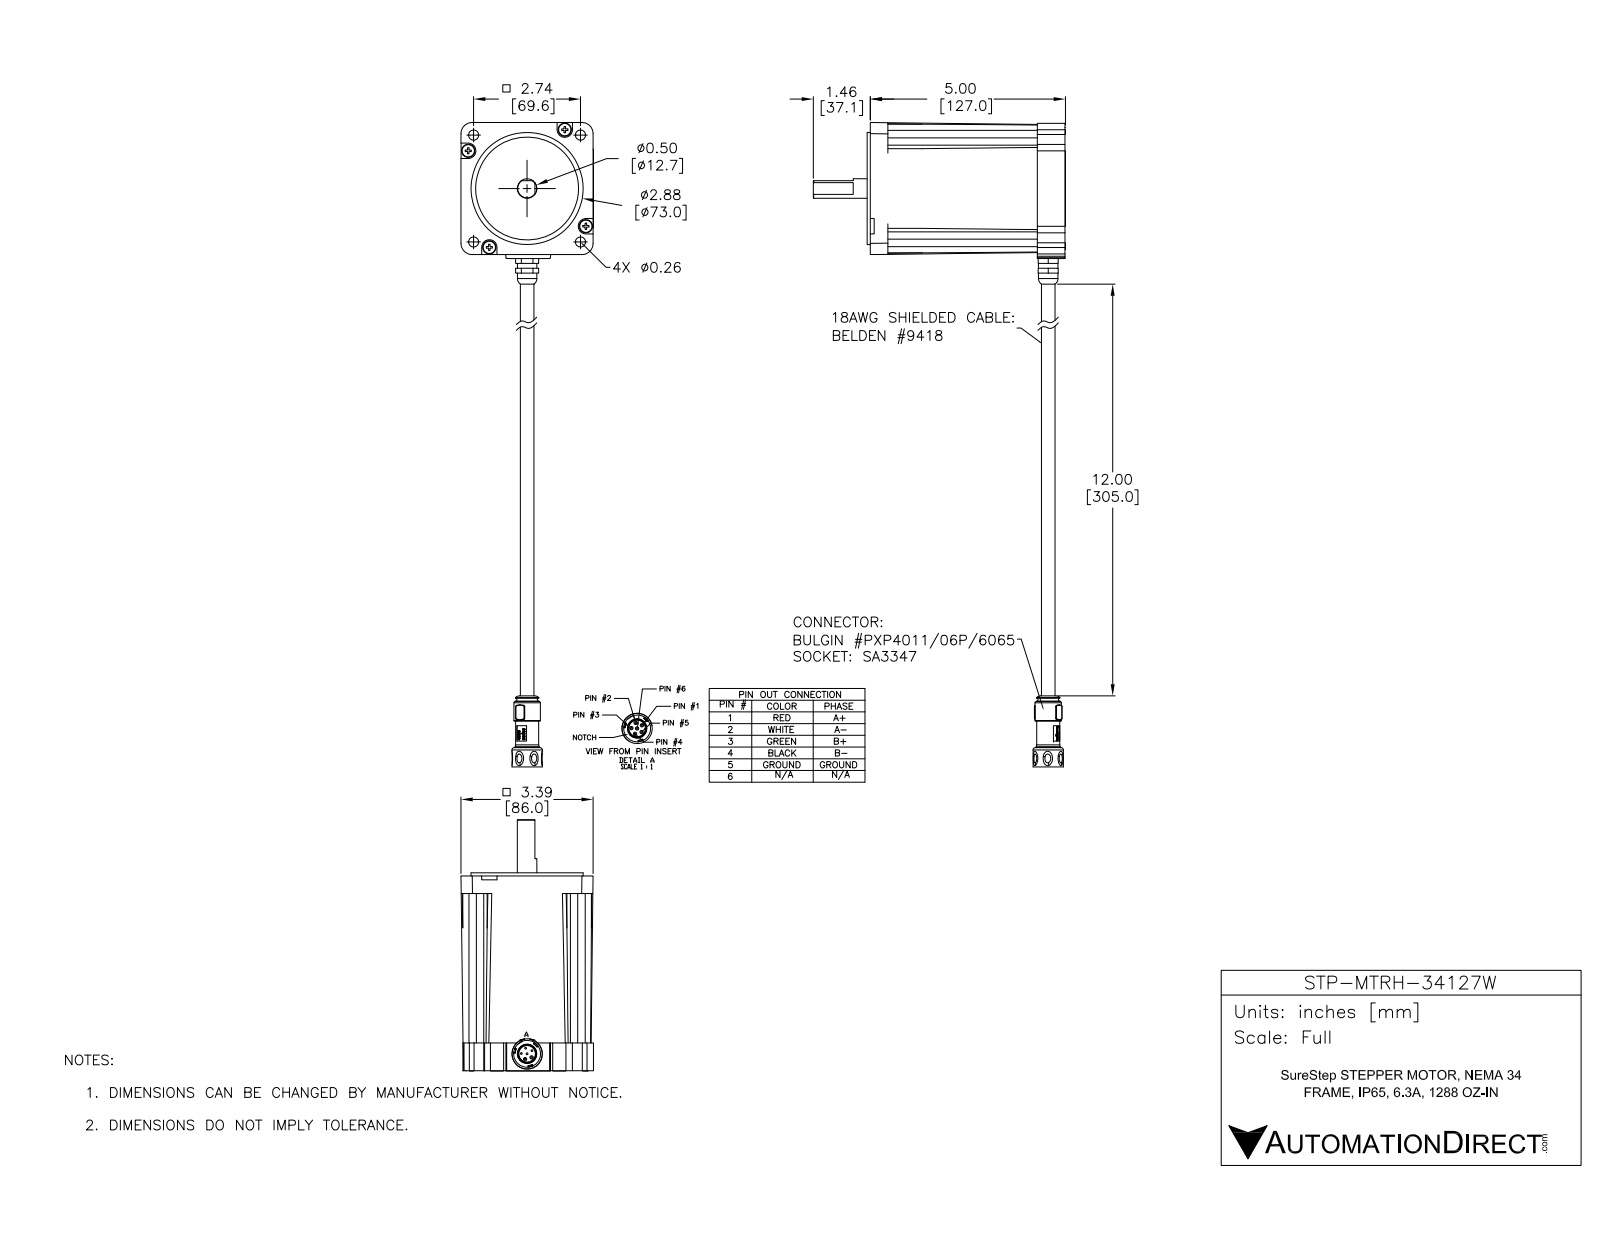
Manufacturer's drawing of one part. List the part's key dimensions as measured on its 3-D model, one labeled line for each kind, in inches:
Part name (STEP PRODUCT): STP-MTRH-34127W
STEP written by: SolidWorks 2017 (AUTOMOTIVE_DESIGN)
Units: inches
Bodies: 3 solids, 840 faces (309 planar, 234 cylindrical, 297 other)
Overall size (bounding box): 16.516 × 6.441 × 3.395
Volume: 52.13 in³ · Surface area: 113.2 in²
Round holes (diameter × count): ⌀0.047 ×6, ⌀0.26 ×4, ⌀0.125 ×1, ⌀0.228 ×1, ⌀0.449 ×1, ⌀0.689 ×1, ⌀0.75 ×1, ⌀2.638 ×1
Round bosses / shafts (diameter × count): ⌀0.05 ×4, ⌀0.5 ×2, ⌀3.125 ×1, ⌀2.875 ×1, ⌀0.777 ×1, ⌀0.674 ×1, ⌀0.613 ×1, ⌀0.592 ×1
Partial cylindrical surfaces — rounded edges, fillets, slot ends (radius × count): R0.005 ×28, R0.008 ×16, R0.02 ×14, R0.065 ×8, R0.188 ×8, R0.388 ×6, R0.187 ×4, R0.197 ×4
Main face-to-face distances: 5.041, 0.04, 5.001, 2.222, 4.991, 5.031, 3.346, 2.782, 0.56, 2.813
Hole centre spacings: 0.148, 0.281, 0.147, 1.937, 2.74, 0.173, 0.174, 3.875
